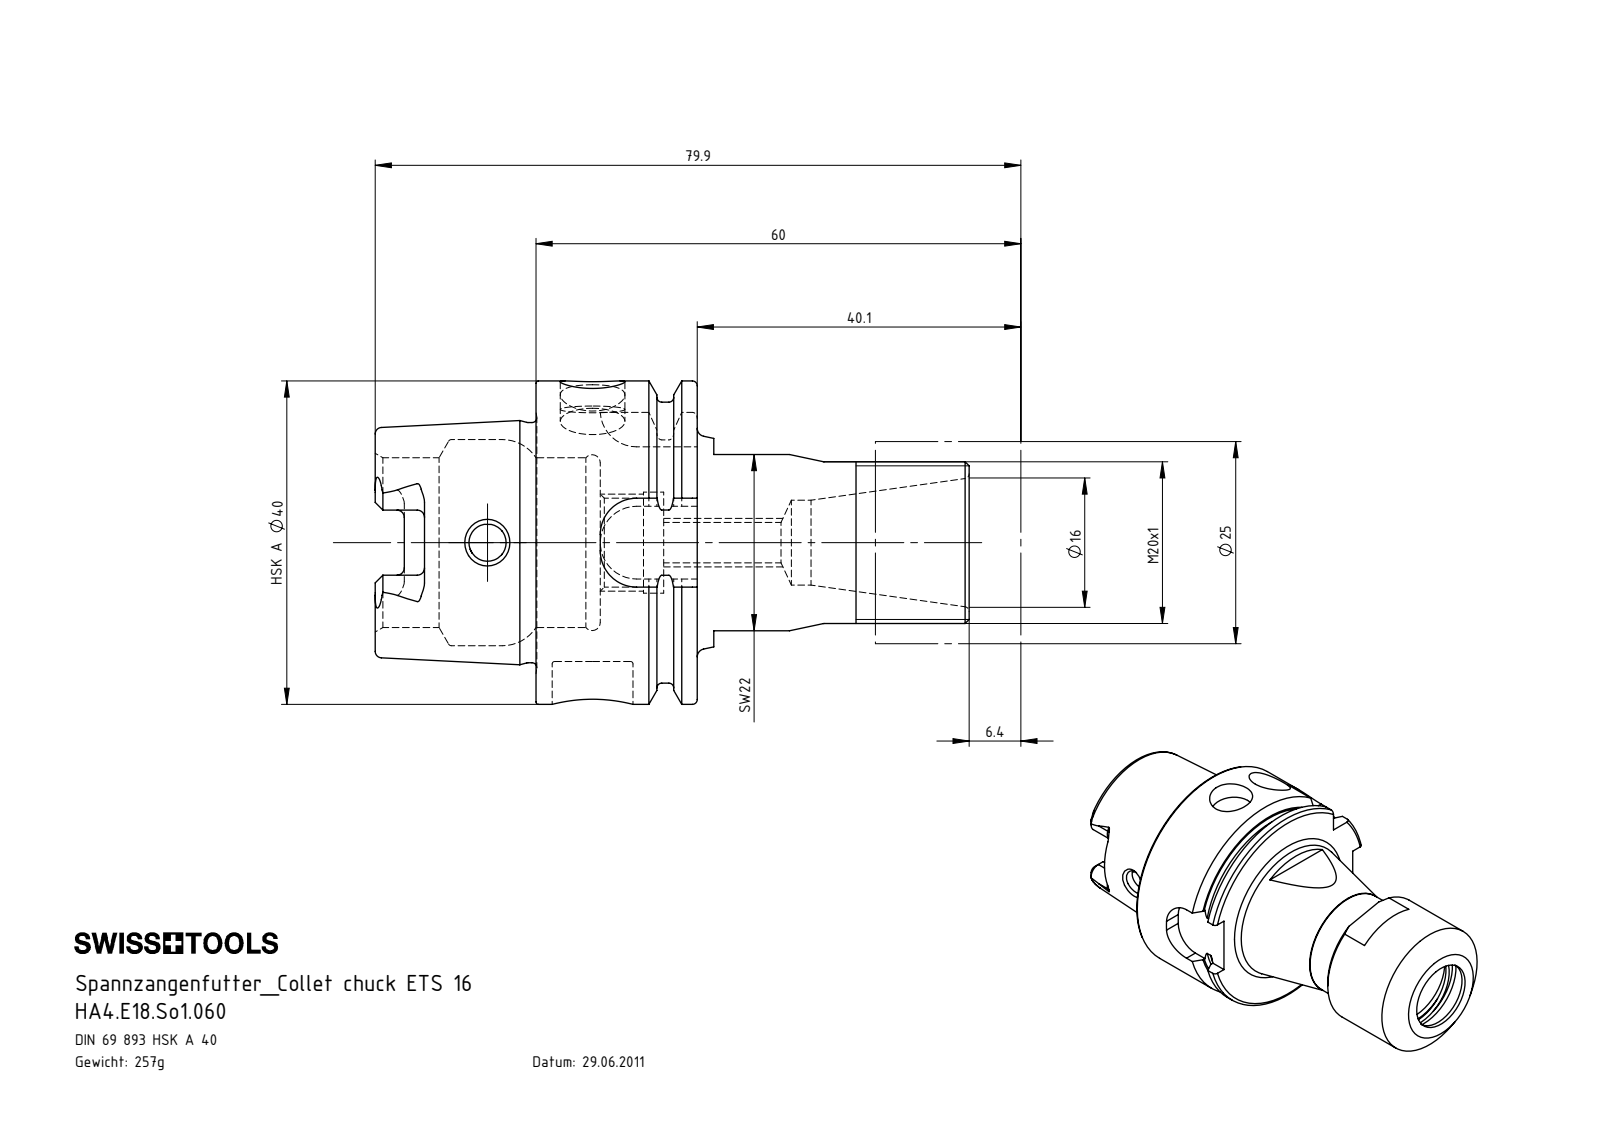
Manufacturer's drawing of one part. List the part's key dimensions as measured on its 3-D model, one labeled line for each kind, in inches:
Part name (STEP PRODUCT): HA4.E18.So1.060
STEP written by: SolidWorks 2017 (AUTOMOTIVE_DESIGN)
Units: inches
Bodies: 1 solid, 133 faces (50 planar, 35 cylindrical, 48 other)
Overall size (bounding box): 2.894 × 1.575 × 1.575
Volume: 1.998 in³ · Surface area: 19.71 in²
Round holes (diameter × count): ⌀0.315 ×2, ⌀0.181 ×1, ⌀0.197 ×1, ⌀0.394 ×1, ⌀0.413 ×1, ⌀0.433 ×1, ⌀0.492 ×1, ⌀0.827 ×1, ⌀1.004 ×1
Round bosses / shafts (diameter × count): ⌀1.575 ×1, ⌀1.368 ×1, ⌀1.17 ×1, ⌀0.787 ×1
Partial cylindrical surfaces — rounded edges, fillets, slot ends (radius × count): R0.035 ×6, R0.074 ×4, R0.177 ×4
Main face-to-face distances: 0.785, 0.313, 0.472, 0.783, 1.096, 1.569, 1.406, 0.622, 0.309, 0.163
